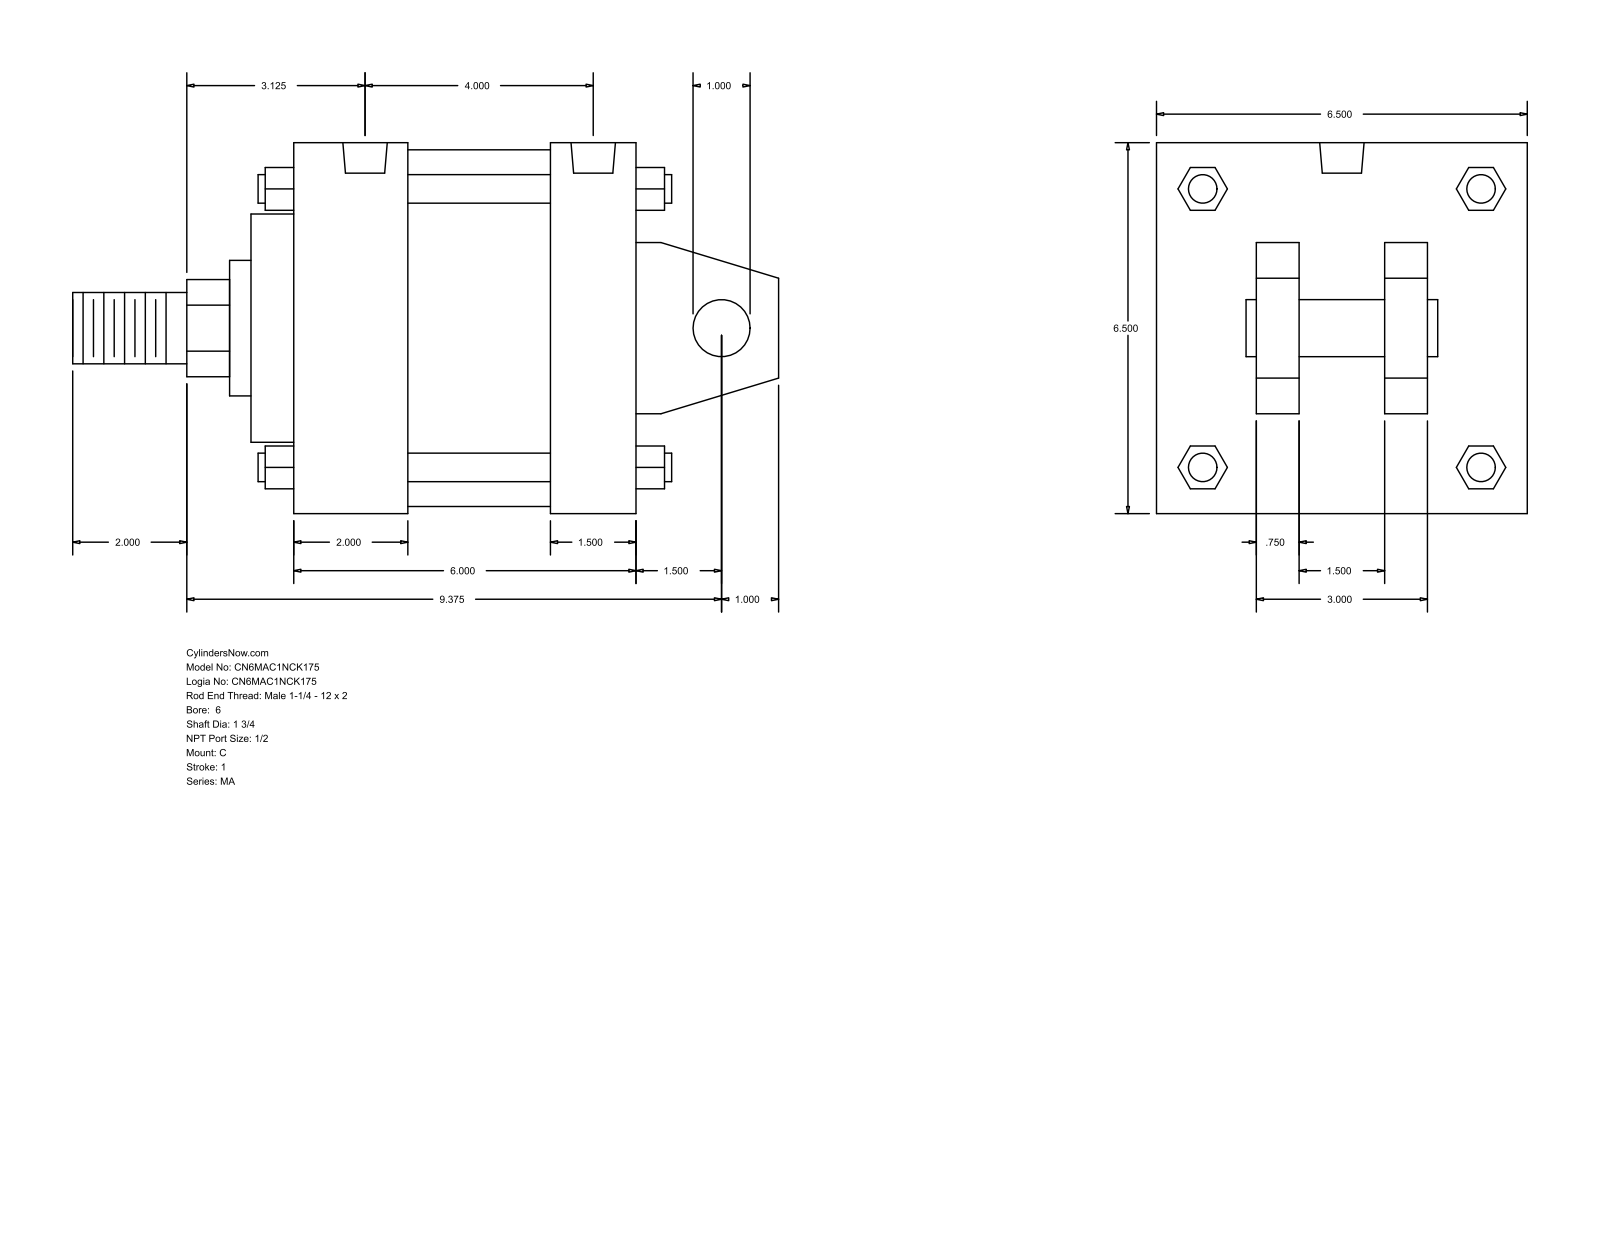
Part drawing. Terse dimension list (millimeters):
name: MA_C__0600_1.75
written by: GSSL Pune (CONFIG_CONTROL_DESIGN)
unit: mm
bodies: 0 solids, 141 faces (109 planar, 32 cylindrical, 0 other)
size: 314.32 × 165.1 × 165.1
holes: 4× ⌀17.46, 2× ⌀19.77
bosses: 4× ⌀12.7, 1× ⌀158.75, 1× ⌀101.6, 1× ⌀60.33, 1× ⌀44.45, 1× ⌀31.75, 1× ⌀25.4
rounds: 1× R21.63
face distances: 165.1, 152.41, 19.05, 38.1, 63.5, 101.6, 50.8, 44.45, 120.65, 57.15
hole spacings: 101.59
